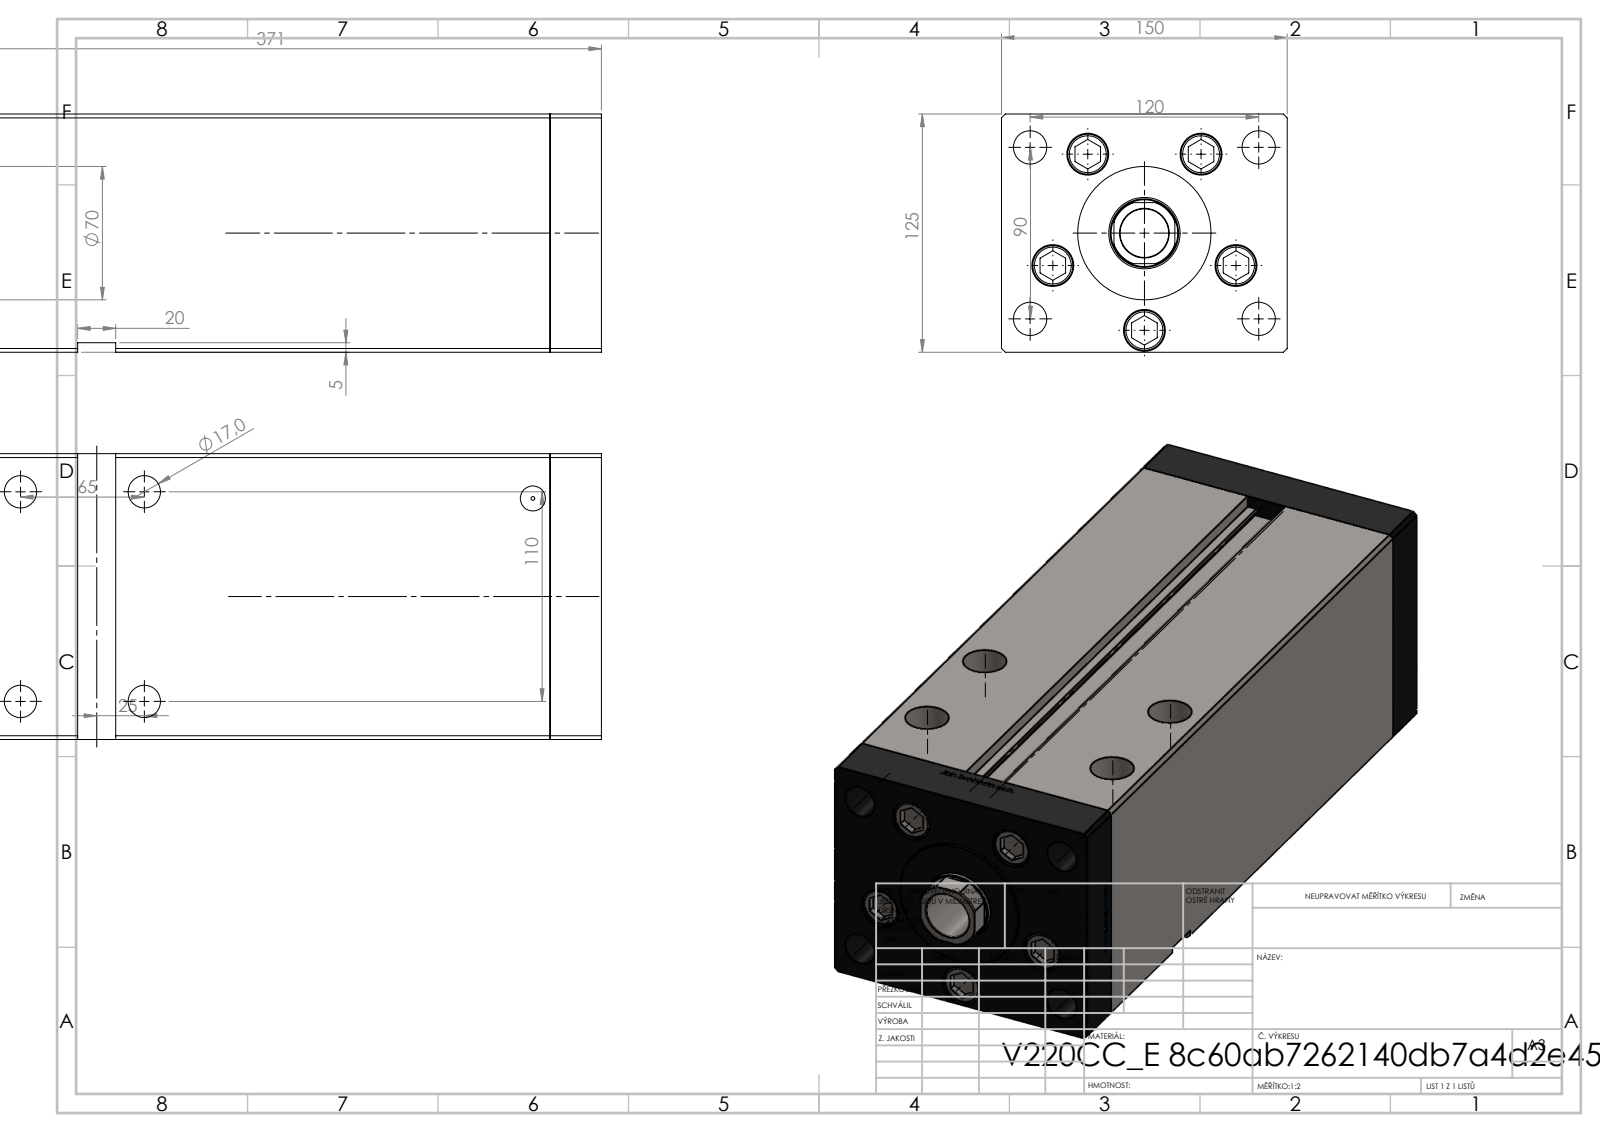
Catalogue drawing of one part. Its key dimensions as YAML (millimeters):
part_name: "V220C_E MIDDLE; V220C_FRONT_E; V220C BACK_E; ALLEN BOLT (+1 more)"
step_written_by: "SolidWorks 2019 (CONFIG_CONTROL_DESIGN)"
units: millimeters
bodies: {solids: 14, faces: 1214, planar: 475, cylindrical: 165, other: 574}
overall_size: [386, 150, 125]
volume: 5602000
surface_area: 537047
round_holes:
  - {diameter: 17.5, count: 9}
  - {diameter: 22, count: 5}
  - {diameter: 17, count: 4}
  - {diameter: 23, count: 4}
  - {diameter: 2, count: 2}
  - {diameter: 13.16, count: 2}
  - {diameter: 25.5, count: 1}
  - {diameter: 36, count: 1}
  - {diameter: 37.5, count: 1}
round_bosses_or_shafts:
  - {diameter: 21, count: 5}
  - {diameter: 8, count: 5}
  - {diameter: 80, count: 1}
  - {diameter: 70, count: 1}
partial_cylinders:
  - {radius: 0.93, count: 2}
  - {radius: 17.5, count: 1}
face_to_face_distances: [125, 150, 27, 344, 317, 33.5, 6.5, 371, 310.5, 337.5]
hole_center_spacings: [51, 75, 30.43, 30.48, 58.89, 60.3, 61.25, 63.14]
